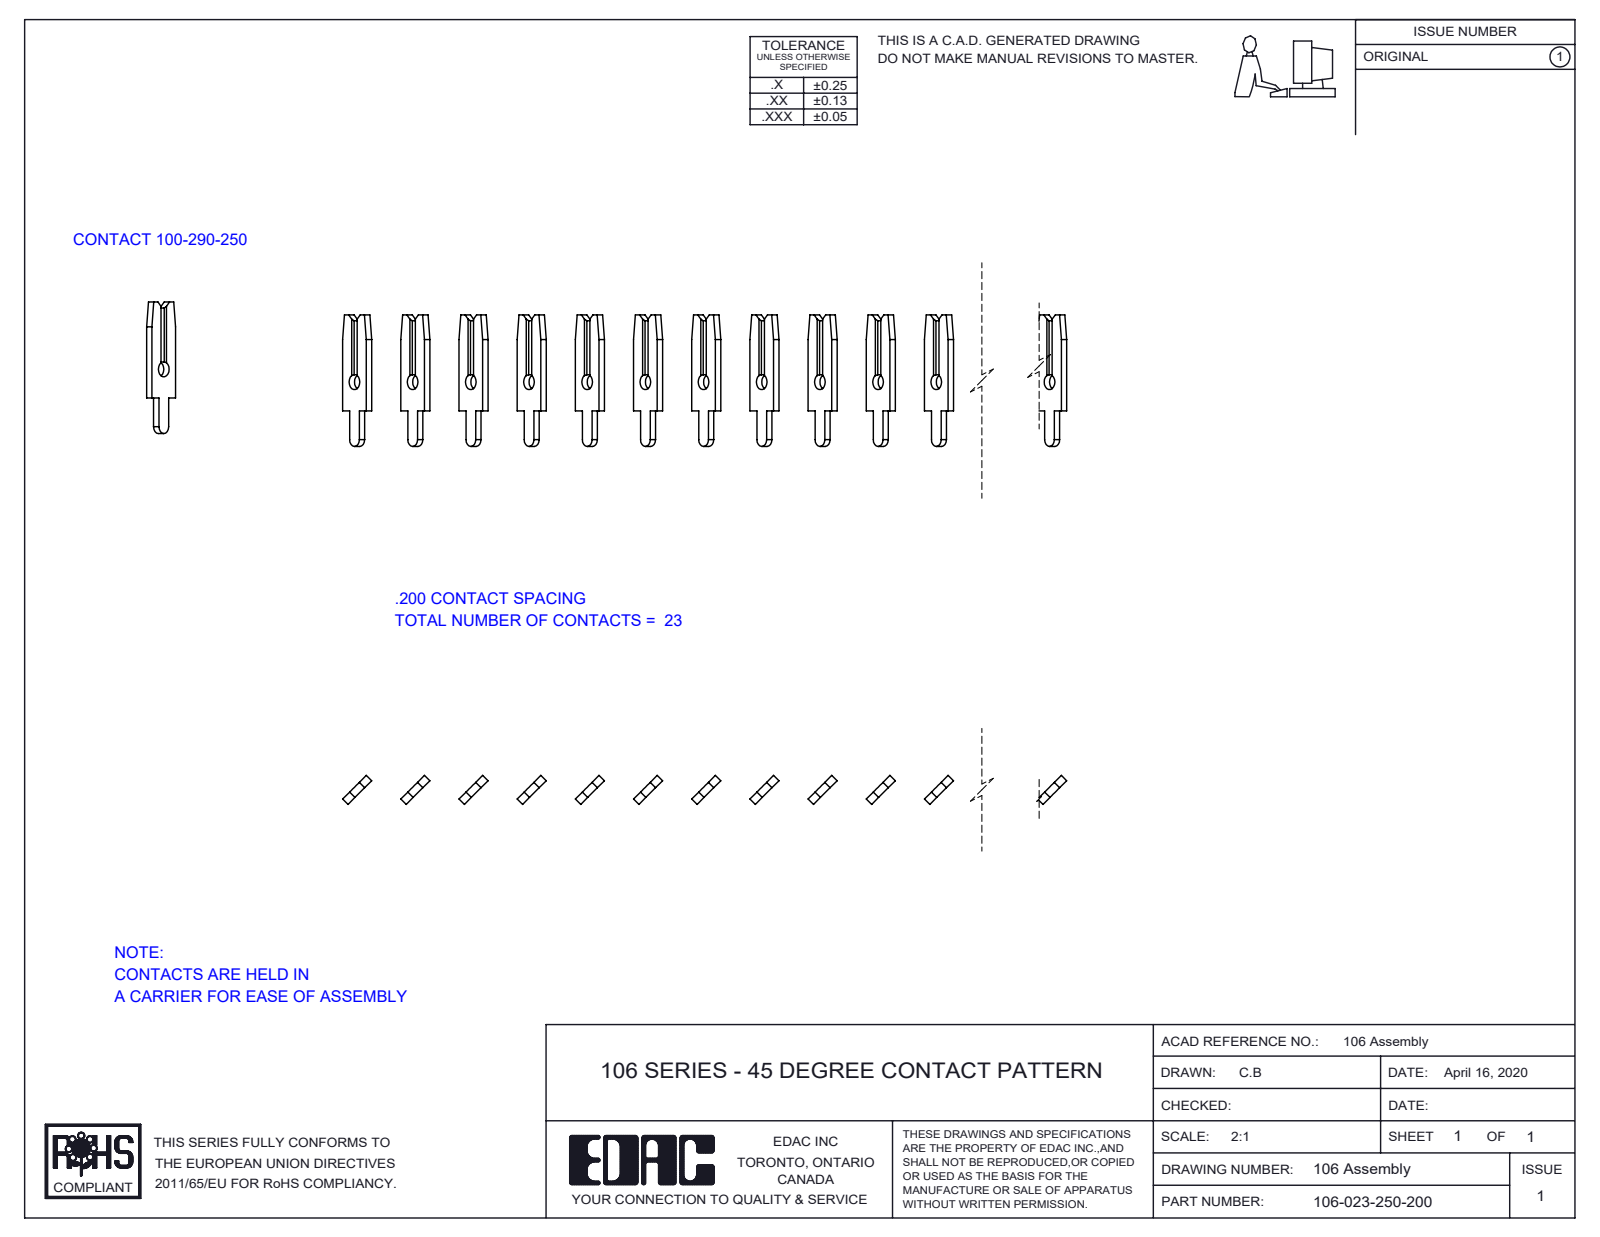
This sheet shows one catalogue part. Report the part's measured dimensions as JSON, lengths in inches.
{"part_name": "100-290-001_100-290-250; 106-023-250-200", "step_written_by": "SolidWorks 2016 (CONFIG_CONTROL_DESIGN)", "units": "inches", "bodies": {"solids": 23, "faces": 552, "planar": 460, "cylindrical": 92, "other": 0}, "overall_size": [4.5, 0.452, 0.1], "volume_in3": 0.022, "surface_area_in2": 2.615, "round_holes": [[0.052, 23]], "partial_cylinders_radius": [[0.024, 23]], "face_to_face_distances": [0.141, 0.848, 0.283, 0.707, 0.99, 0.566, 1.131, 0.424, 0.424, 1.556], "hole_center_spacings": [0.141, 0.283, 0.424, 1.131, 1.556, 0.848, 1.697, 1.839]}
